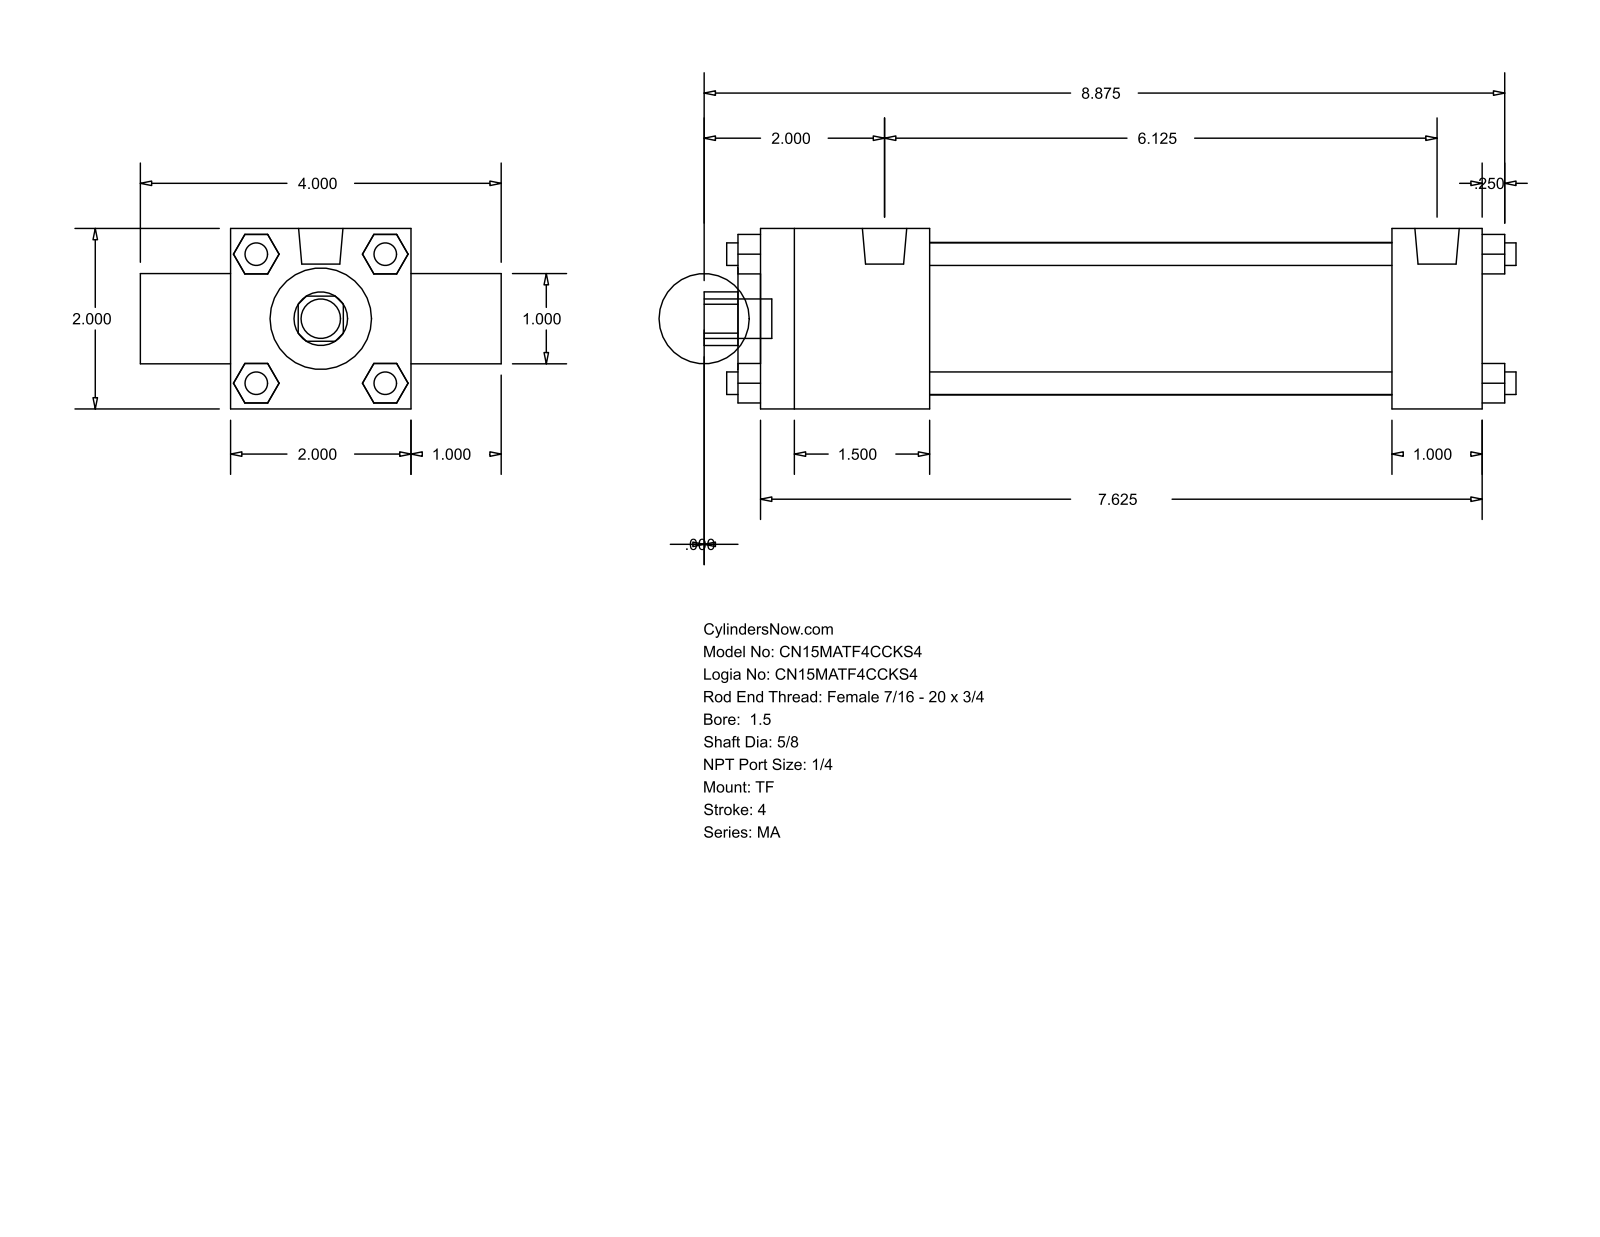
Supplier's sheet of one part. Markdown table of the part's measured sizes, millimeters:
| quantity | value |
| --- | --- |
| part name | MA_TF__0150_0.625 |
| STEP written by | GSSL Pune (CONFIG_CONTROL_DESIGN) |
| units | millimeters |
| bodies | 0 solids, 120 faces (92 planar, 28 cylindrical, 0 other) |
| overall size | 228.6 × 101.6 × 50.8 |
| round holes (diameter × count) | 15.88 × 1, 25.4 × 1, 28.57 × 1, 42.93 × 1 |
| round bosses / shafts (diameter × count) | 6.35 × 4, 7.94 × 3, 12.49 × 2, 11.11 × 1 |
| partial cylindrical surfaces (radius × count) | 7.54 × 1 |
| main face-to-face distances | 50.8, 203.19, 25.4, 76.2, 47.62, 177.8, 130.18, 155.57, 25.39, 6.35 |
